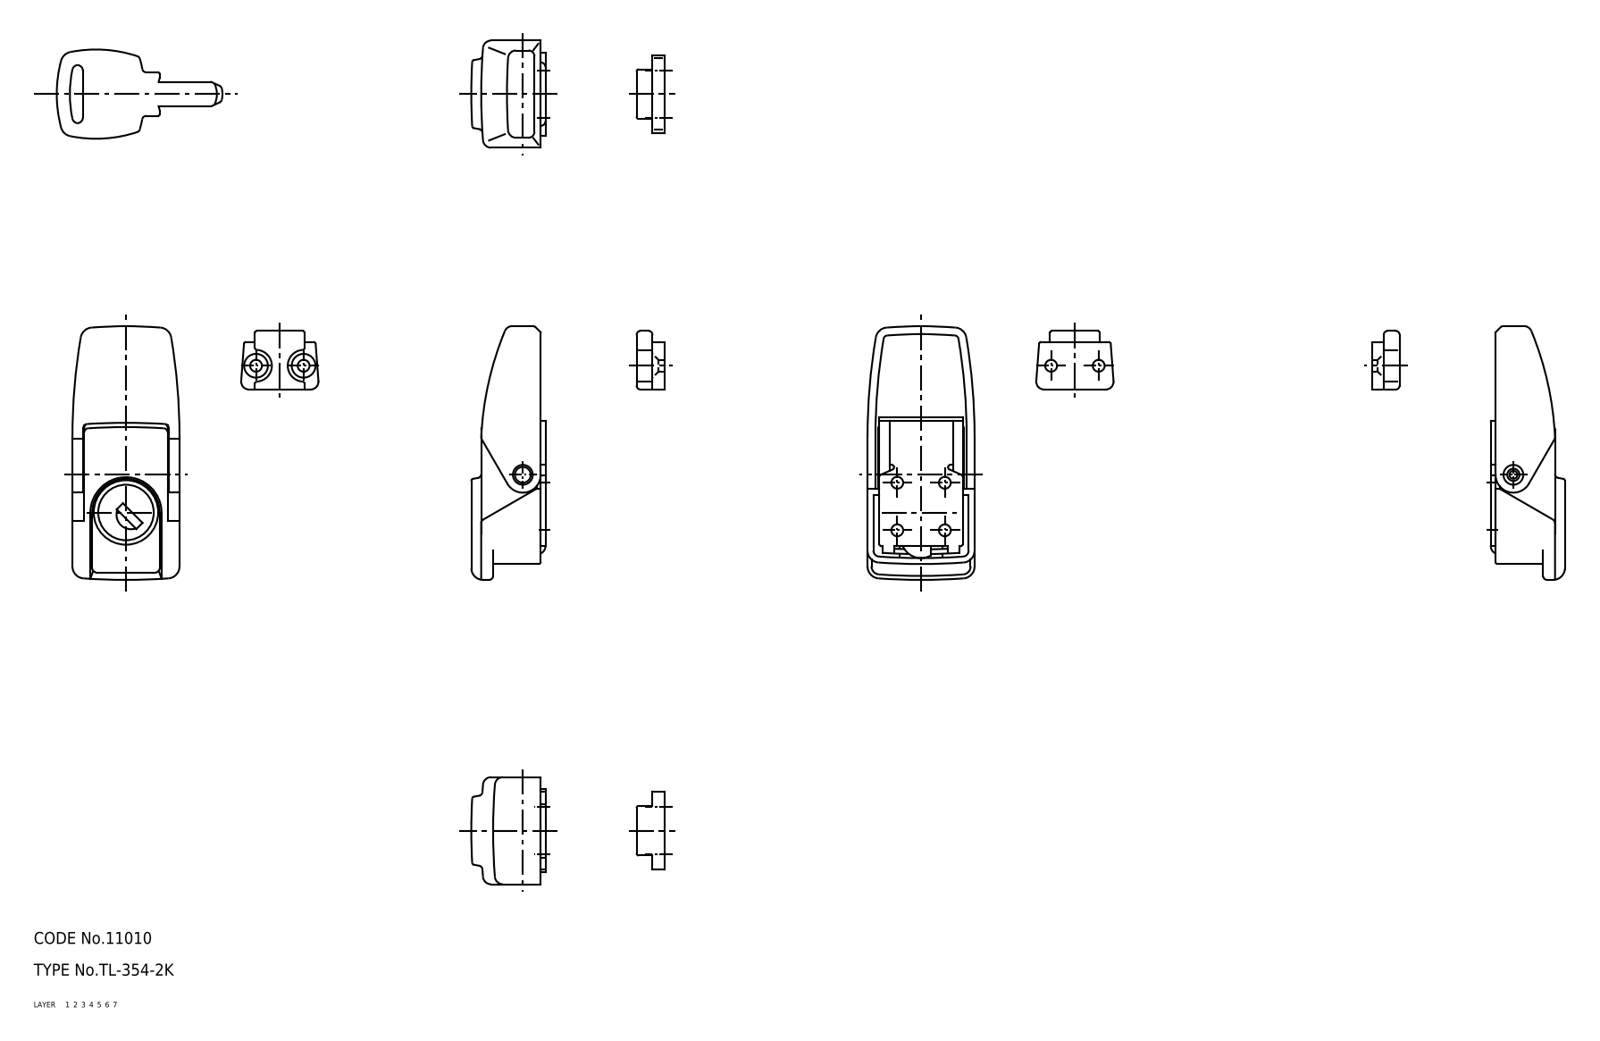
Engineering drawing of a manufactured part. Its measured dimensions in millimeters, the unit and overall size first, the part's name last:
Units: millimetres
Overall size (bounding box): 90.55 × 64.01 × 27
Volume: 16 478 mm³ · Surface area: 15 409 mm²
Bodies: 9 solids, 344 faces (0 planar, 0 cylindrical, 344 other)
Part name (STEP PRODUCT): lock cam; shaft_A; shaft_B; lock (+6 more)
STEP written by: CADfix (AUTOMOTIVE_DESIGN)
